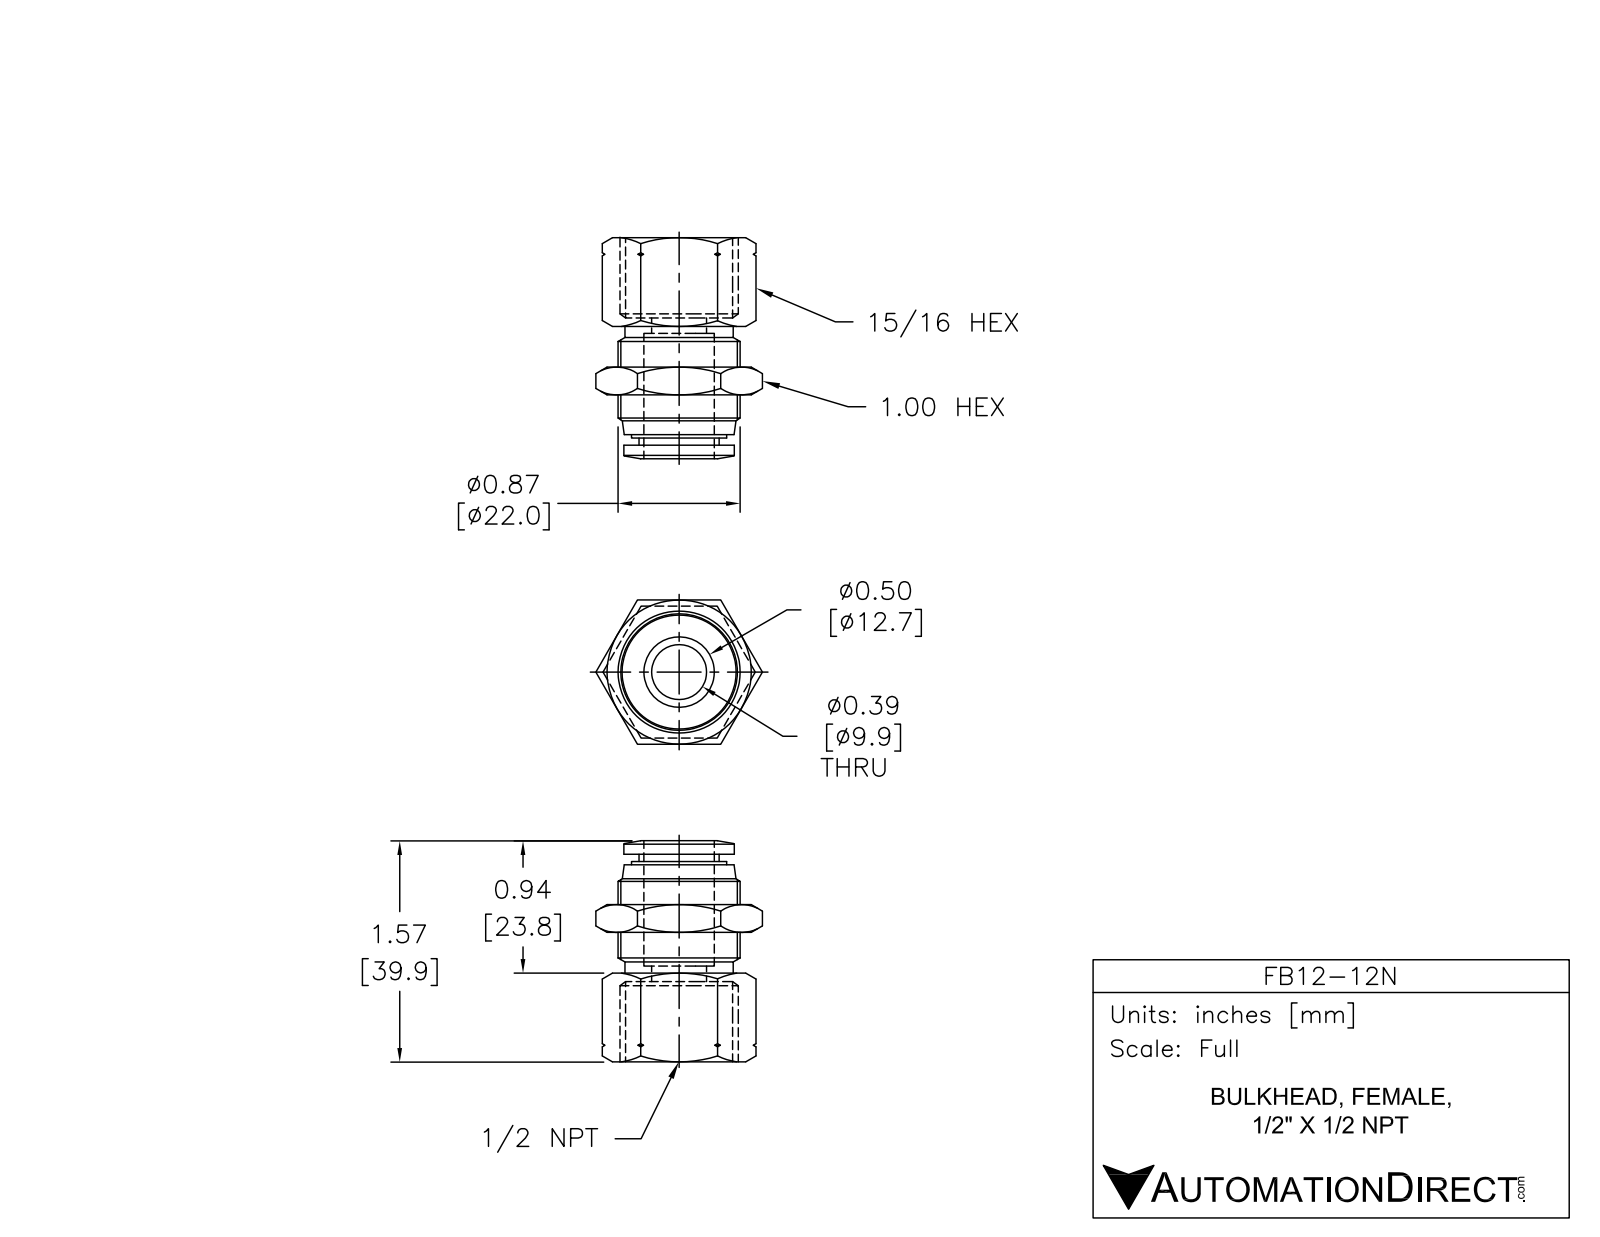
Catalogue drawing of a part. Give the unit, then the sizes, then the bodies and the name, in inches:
Units: inches
Overall size (bounding box): 1.569 × 1.182 × 1.024
Round holes (diameter × count): ⌀0.394 ×1, ⌀0.51 ×1
Round bosses / shafts (diameter × count): ⌀0.866 ×1, ⌀0.783 ×1, ⌀0.709 ×1, ⌀0.675 ×1, ⌀0.569 ×1
Main face-to-face distances: 0.945, 0.039, 0.984, 0.059, 1.024, 0.348, 0.289, 0.544, 0.485, 0.197
Volume: 0.535 in³ · Surface area: 10.02 in²
Bodies: 1 solid, 95 faces (21 planar, 16 cylindrical, 58 other)
Part name (STEP PRODUCT): FB12-12N
STEP written by: SolidWorks 2015 (AUTOMOTIVE_DESIGN)
